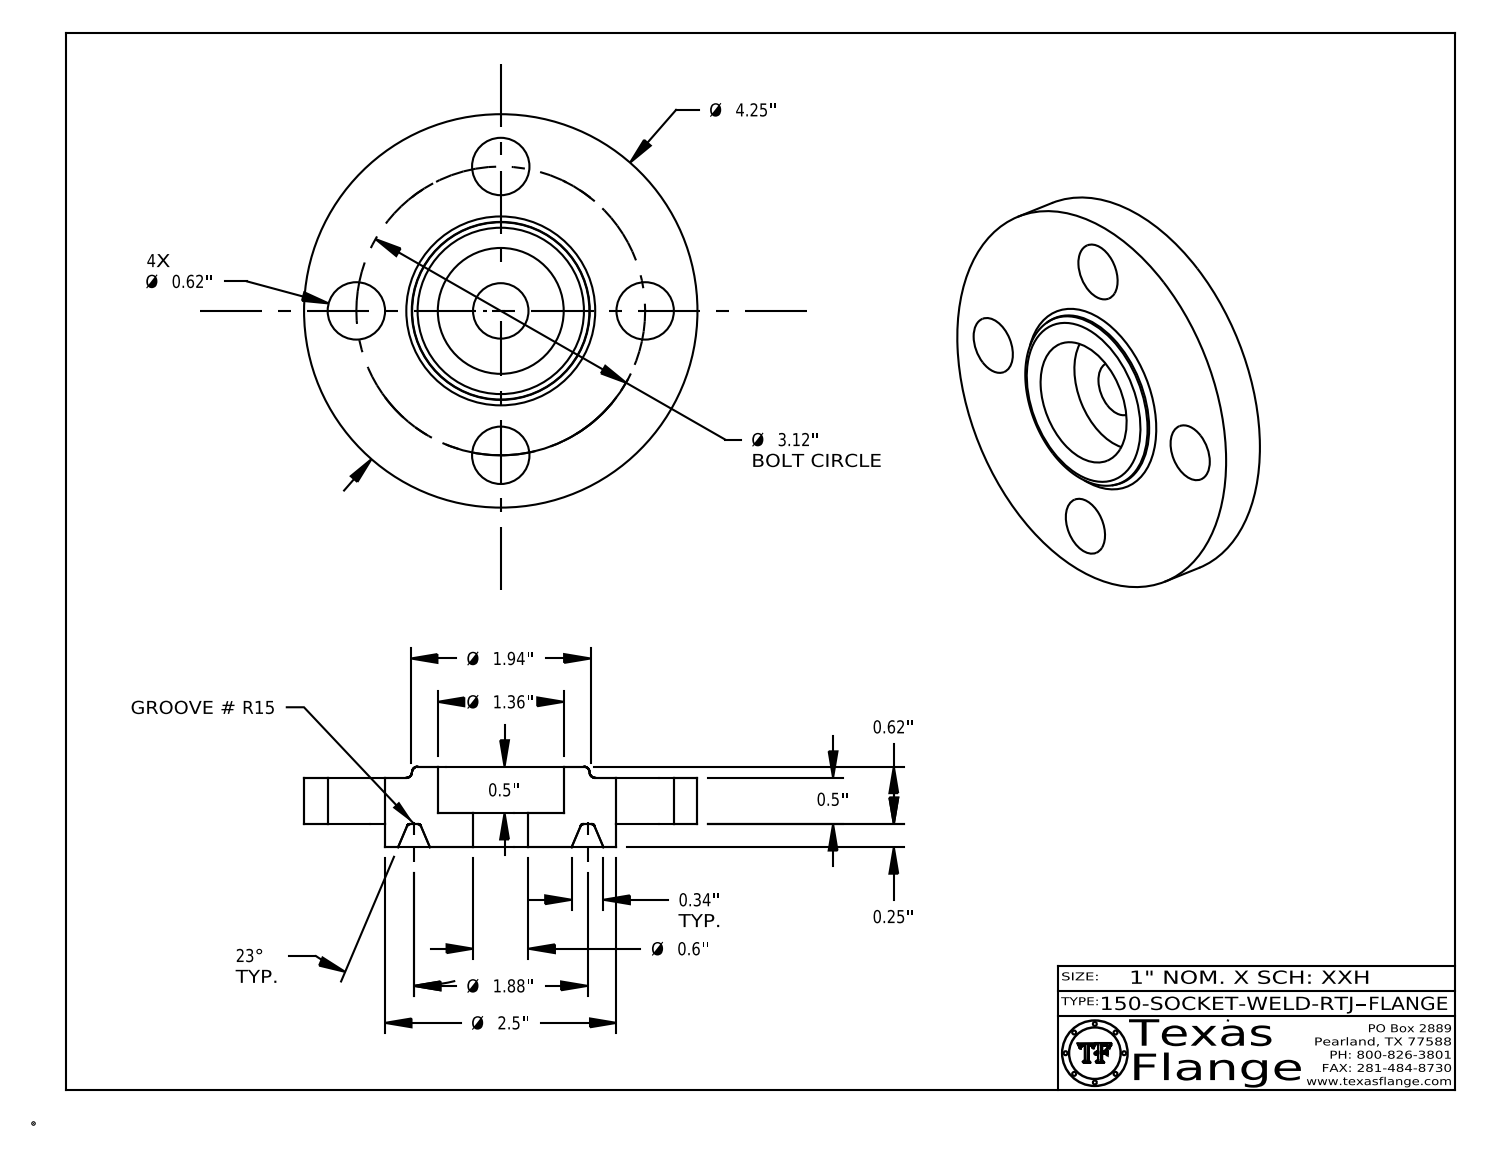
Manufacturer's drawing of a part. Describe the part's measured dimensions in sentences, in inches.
The part is named "150-SOCKET-WELD-RTJ". Its 3-D file was written by "CATIA V5 STEP AP214 (AUTOMOTIVE_DESIGN)". It is 1 solid with 422 faces: 372 planar, 36 cylindrical and 14 other. Overall it measures 4.25 by 4.25 by 0.87 inches. Its volume is 6.883 cubic inches and its surface area 43.15 square inches. Round holes: 4 of diameter 0.62, 1 of diameter 0.495, 1 of diameter 0.599, 1 of diameter 1.36. Round bosses or shafts: 8 of diameter 0.03, 1 of diameter 4.25, 1 of diameter 2.5, 1 of diameter 0.39. The main face-to-face distances are 0.5, 0.25, 0.75, 0.12, 0.37, 0.38, 0.87, 0.62, 0.735, 0.485. The hole center spacings are 1.56, 2.206, 1.194, 2.882, 3.12, 1.56.
